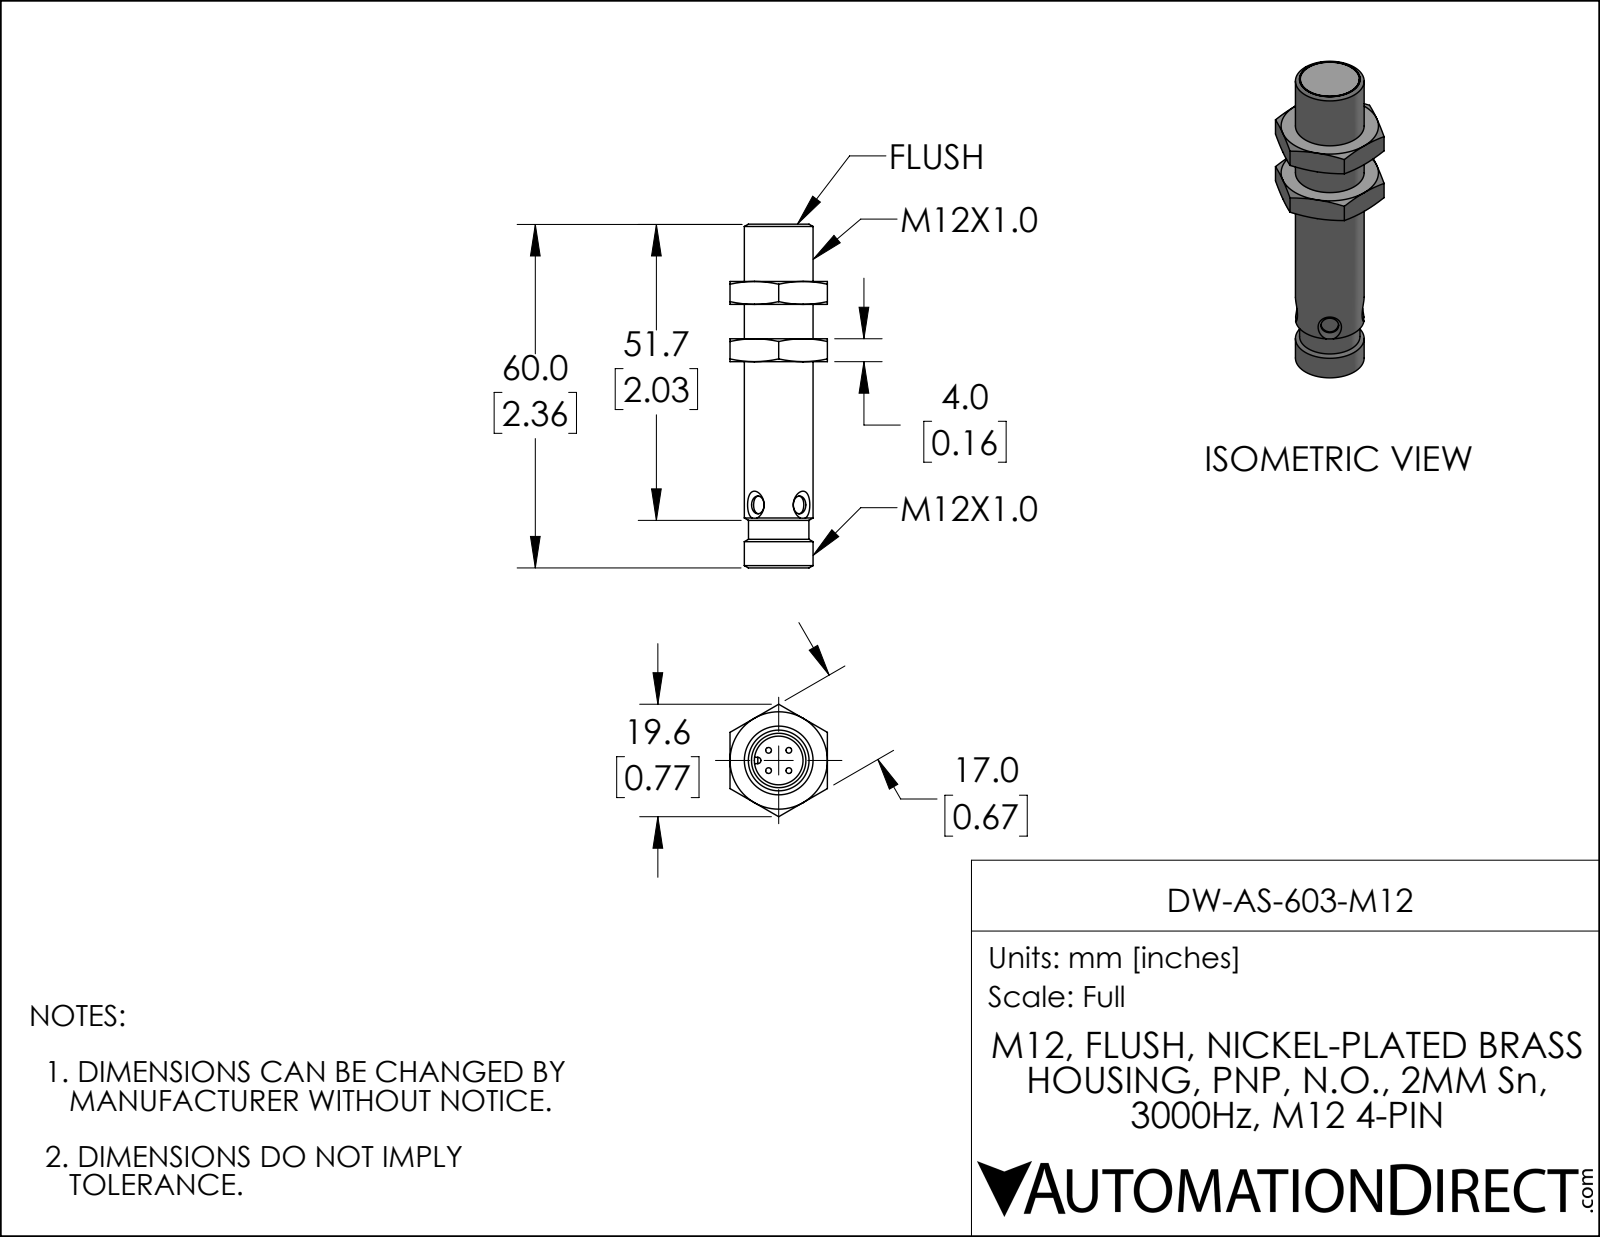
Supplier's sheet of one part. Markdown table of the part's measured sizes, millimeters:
| quantity | value |
| --- | --- |
| part name | DW-AS-603-M12 |
| STEP written by | SolidWorks 2019 (AUTOMOTIVE_DESIGN) |
| units | millimeters |
| bodies | 1 solid, 83 faces (23 planar, 22 cylindrical, 38 other) |
| overall size | 60 × 19.6 × 17 |
| volume | 7 260 mm³ |
| surface area | 3 516 mm² |
| round holes (diameter × count) | 3.1 × 2, 8.5 × 1, 10.5 × 1 |
| round bosses / shafts (diameter × count) | 1 × 4, 12 × 1, 10.5 × 1, 10.3 × 1 |
| partial cylindrical surfaces (radius × count) | 0.6 × 2, 4.9 × 1 |
| main face-to-face distances | 10, 4, 17, 14, 6, 20, 24, 51.4, 41.4, 37.4 |
